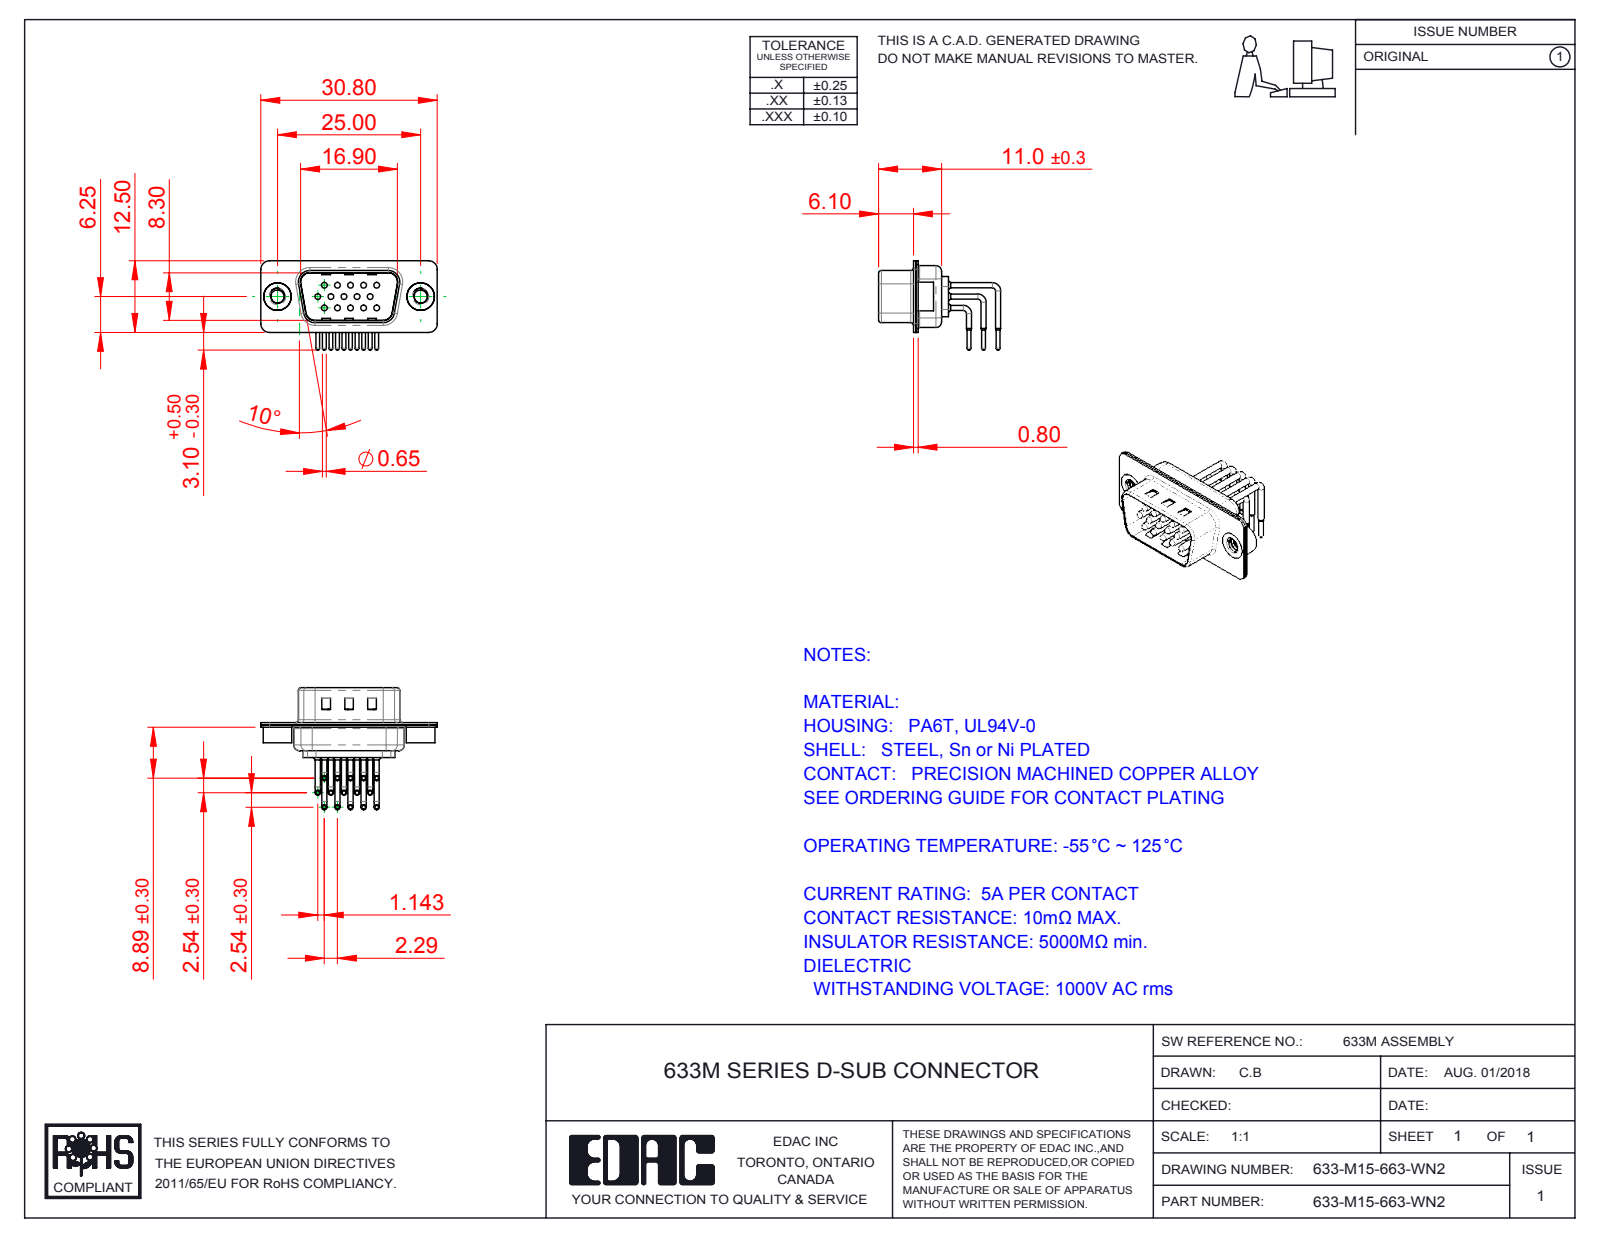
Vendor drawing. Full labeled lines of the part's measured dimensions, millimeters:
Part name (STEP PRODUCT): 633M 4-40 Threaded Rivet; 633M Housing_15 Contacts; 633-M15-663-WN2; 633M Contact Row 2 (+4 more)
STEP written by: SolidWorks 2016 (CONFIG_CONTROL_DESIGN)
Units: millimetres
Bodies: 20 solids, 1954 faces (1067 planar, 669 cylindrical, 218 other)
Overall size (bounding box): 30.8 × 21.32 × 15.6
Volume: 1 451 mm³ · Surface area: 4 630 mm²
Round holes (diameter × count): ⌀1 ×15, ⌀1.7 ×15, ⌀2 ×15, ⌀2.26 ×2, ⌀4 ×2, ⌀4.8 ×2
Round bosses / shafts (diameter × count): ⌀0.9 ×30, ⌀1.5 ×15, ⌀0.65 ×15, ⌀5 ×2, ⌀4.9 ×2
Partial cylindrical surfaces — rounded edges, fillets, slot ends (radius × count): R1.5 ×16, R1.01 ×15, R2 ×12, R0.5 ×8, R1.6 ×8, R0.25 ×4, R0.6 ×4, R0.65 ×4
Main face-to-face distances: 0.4, 0.85, 0.8, 9.55, 1.25, 10.4, 1.5, 8.7, 1.9, 0.35
Hole centre spacings: 3.96, 2.28, 2.29, 4.57, 6.05, 6.86, 7.92, 6.04
